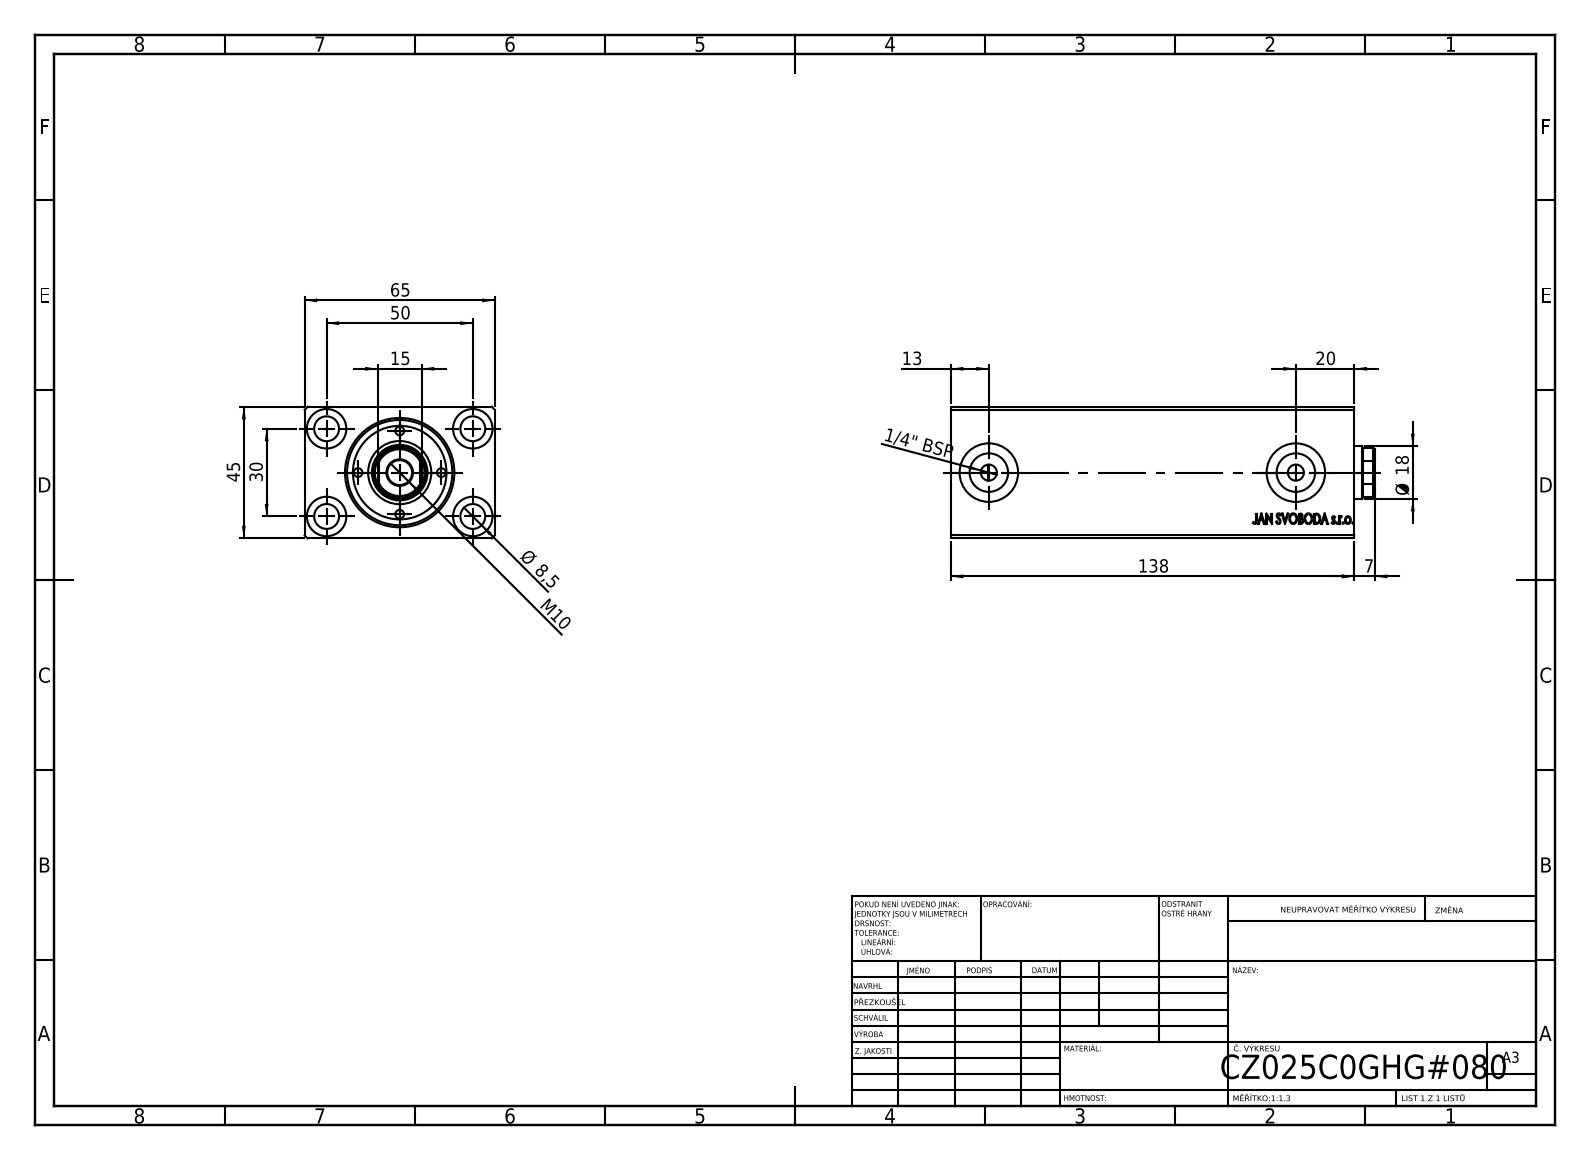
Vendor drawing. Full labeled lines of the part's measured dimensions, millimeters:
STEP written by: SolidWorks 2019 (CONFIG_CONTROL_DESIGN)
Units: millimetres
Bodies: 1 solid, 824 faces (396 planar, 46 cylindrical, 382 other)
Overall size (bounding box): 138 × 65 × 45
Volume: 295 409 mm³ · Surface area: 62 970 mm²
Round holes (diameter × count): ⌀8.5 ×4, ⌀13.5 ×4, ⌀5.5 ×2, ⌀8 ×2, ⌀13.16 ×2, ⌀20 ×2, ⌀25 ×1, ⌀36 ×1
Main face-to-face distances: 45, 65, 138, 137.8, 10.33, 127.67, 7, 130.8, 131, 125.2
Hole centre spacings: 29.15, 30, 50, 58.31, 85, 105
